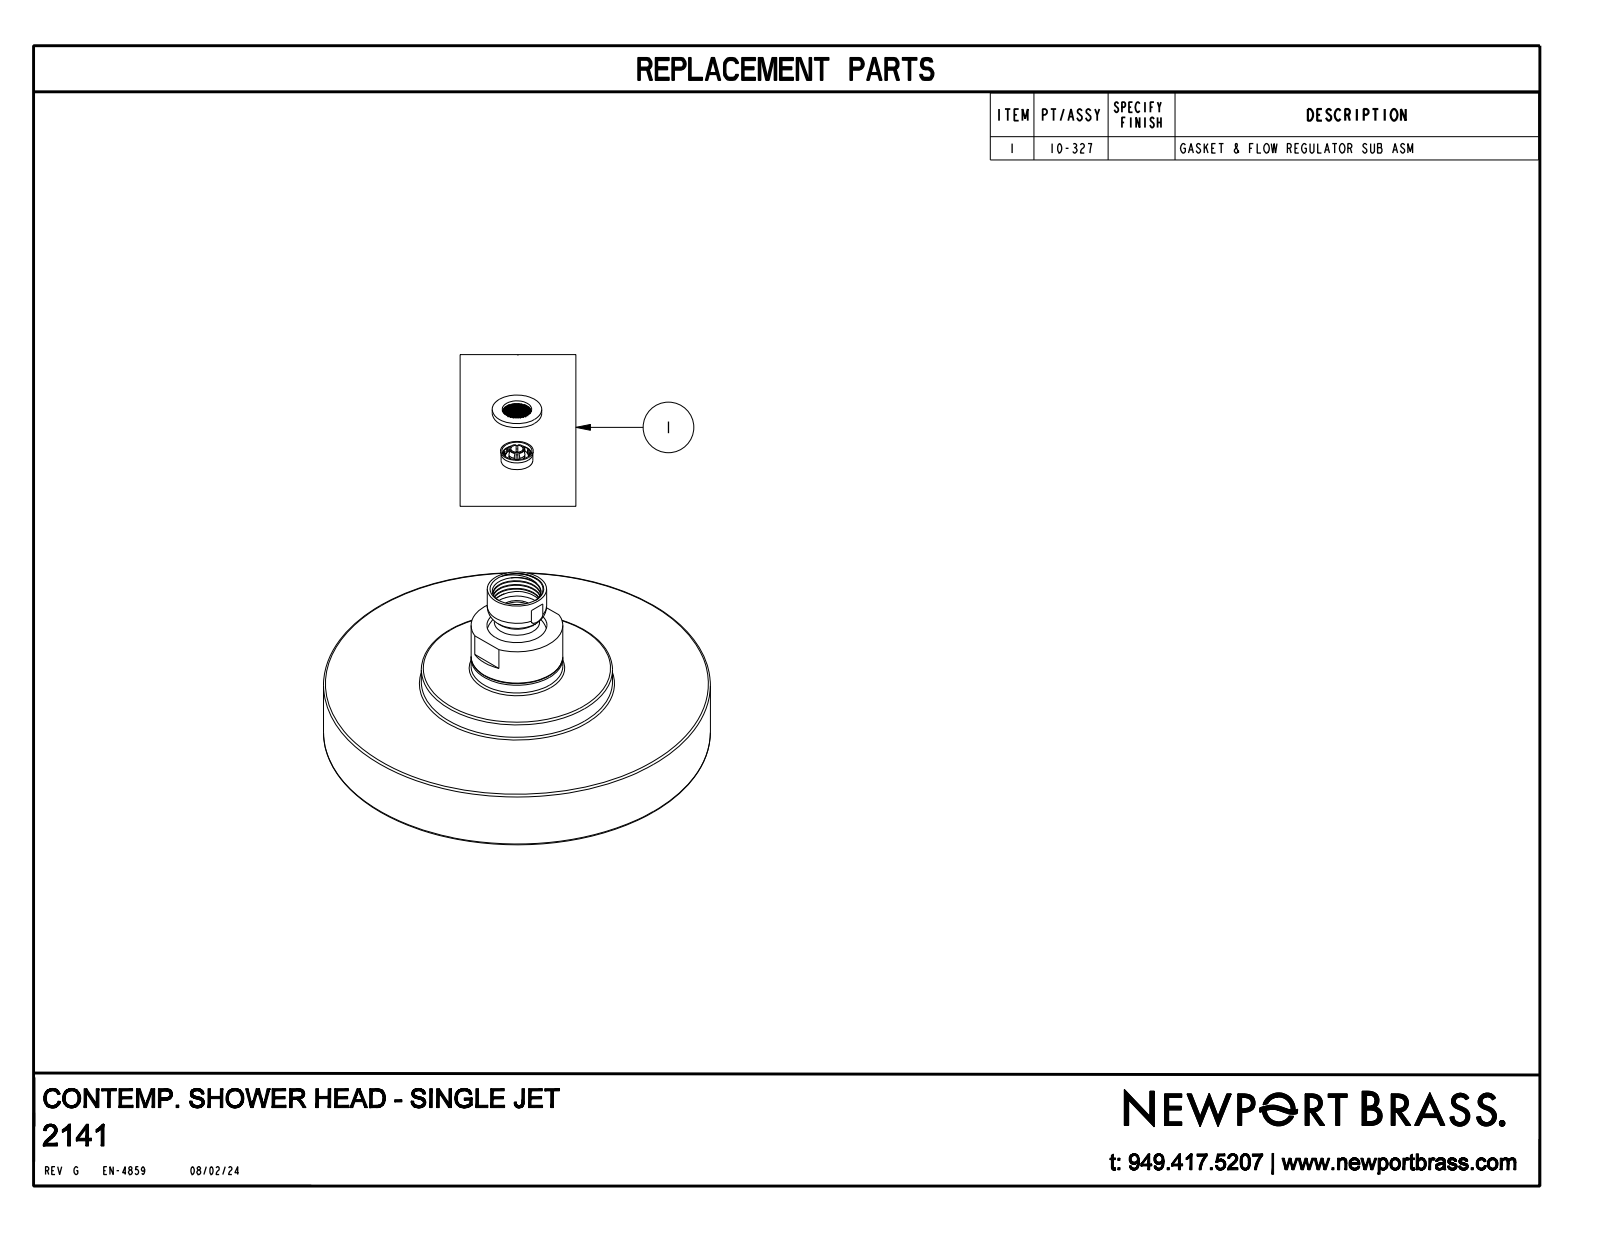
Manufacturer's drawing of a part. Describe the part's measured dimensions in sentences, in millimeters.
The part is named "2141". Its 3-D file was written by "CREO PARAMETRIC BY PTC INC, 2018400 (AUTOMOTIVE_DESIGN)". It is 2 solids with 897 faces: 125 planar, 240 cylindrical and 532 other. Overall it measures 150.1 by 150.1 by 77.8 millimeters. Its volume is 563 900 cubic millimeters and its surface area 62 880 square millimeters. Round holes: 90 of diameter 3.2, 4 of diameter 1.3, 1 of diameter 5.6, 1 of diameter 15.3. Round bosses or shafts: 18 of diameter 5, 1 of diameter 150.1, 1 of diameter 74.2, 1 of diameter 35.6, 1 of diameter 23, 1 of diameter 15.2. The main face-to-face distances are 7.4, 27.5, 20.1, 45.8, 38.4, 18.3, 29.5, 36.9, 57, 75.3. The hole center spacings are 35.8, 24.9, 24.9, 43.1, 52.9, 54.9, 12.4, 46.1.
